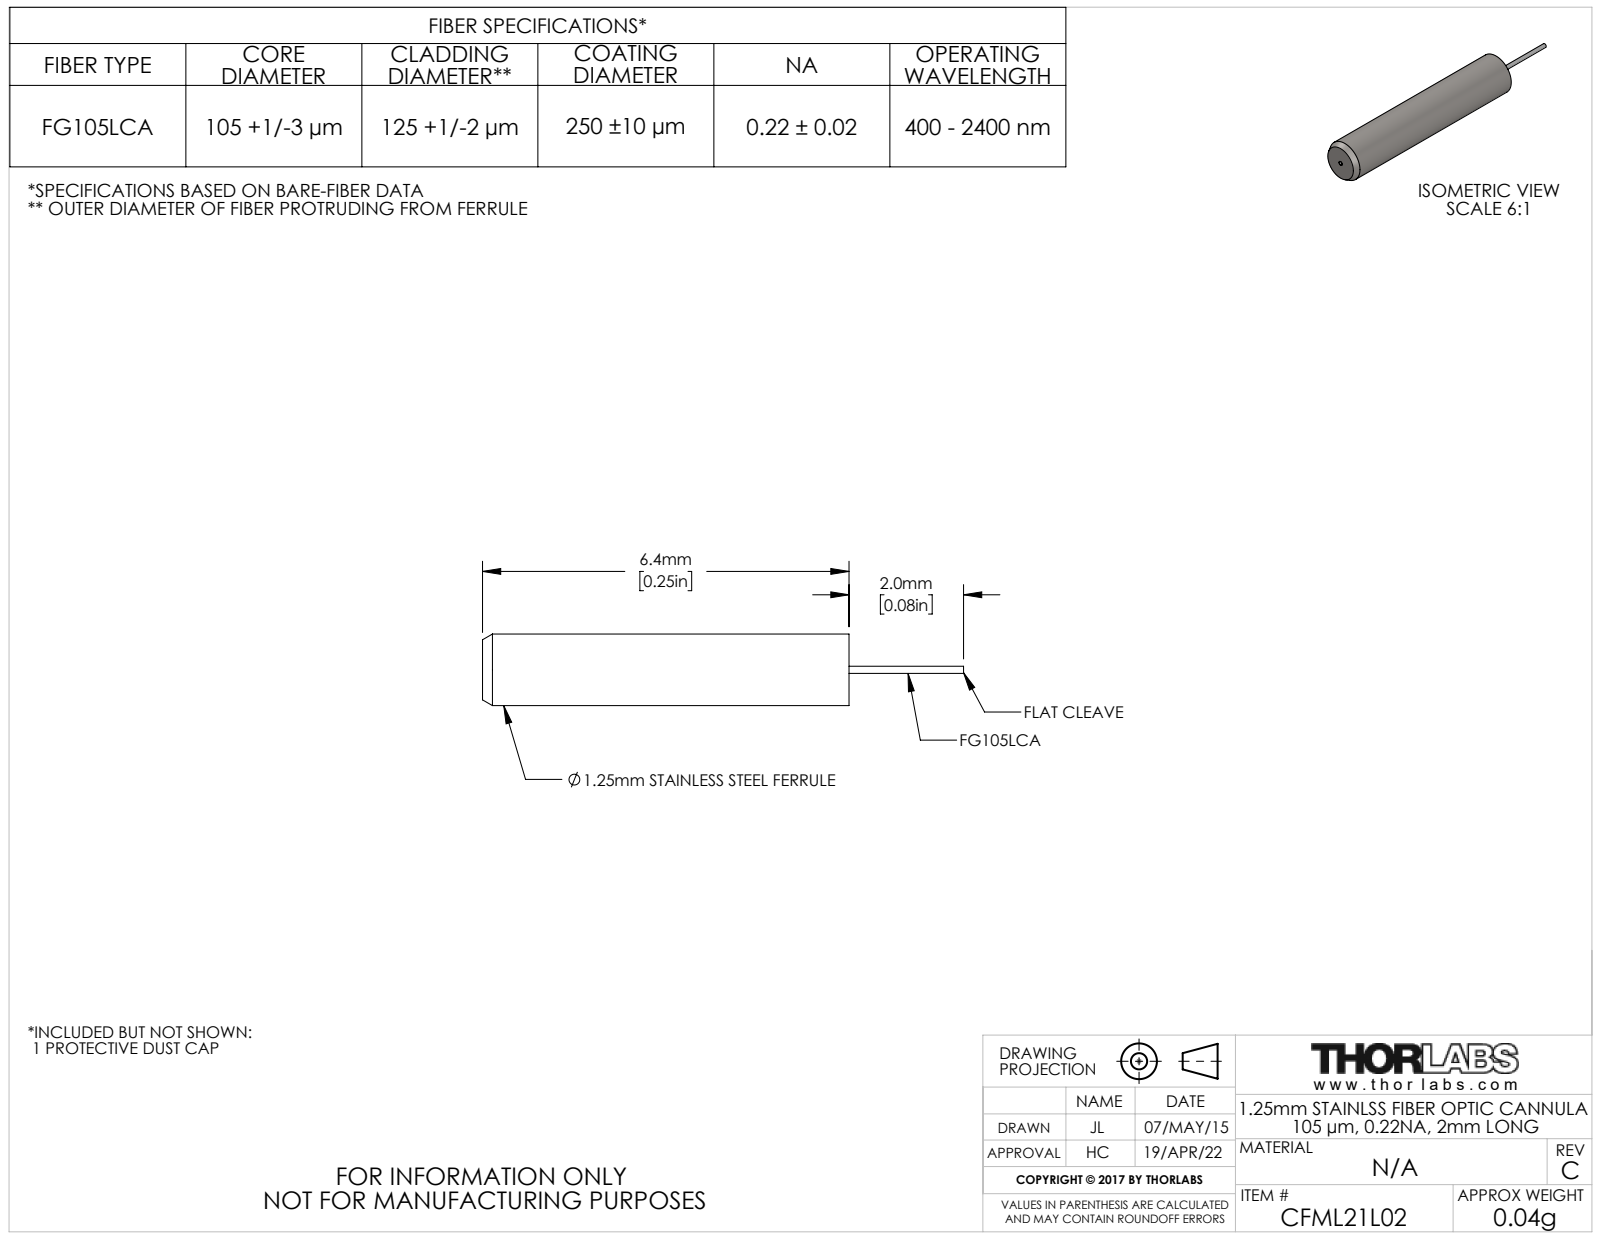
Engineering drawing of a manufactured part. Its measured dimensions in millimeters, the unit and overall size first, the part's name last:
Units: millimetres
Overall size (bounding box): 8.4 × 1.2 × 1.2
Round holes (diameter × count): ⌀1 ×1
Round bosses / shafts (diameter × count): ⌀1.2 ×1
Main face-to-face distances: 6.4, 8.4, 2
Bodies: 2 solids, 18 faces (4 planar, 8 cylindrical, 6 other)
Part name (STEP PRODUCT): TTN041710-E0W
STEP written by: SolidWorks 2014 (CONFIG_CONTROL_DESIGN)
